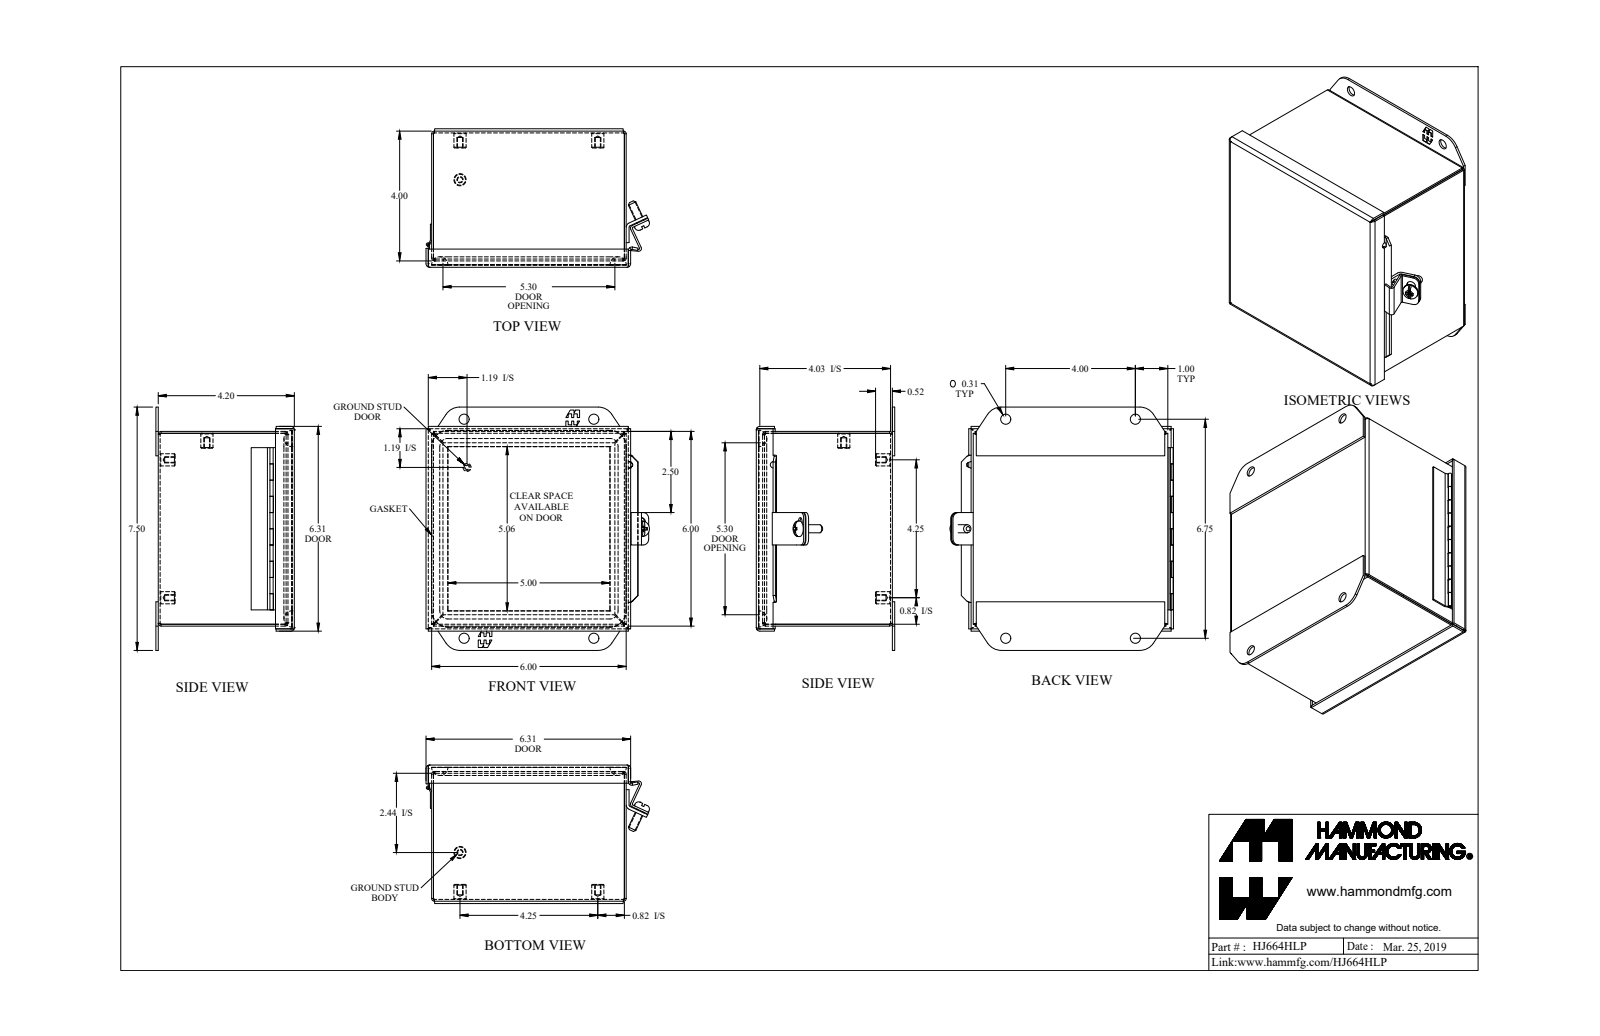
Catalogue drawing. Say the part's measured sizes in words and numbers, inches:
The part is named "HJ664HLP". Its 3-D file was written by "SolidWorks 2018 (AUTOMOTIVE_DESIGN)". It is 16 solids with 566 faces: 305 planar, 163 cylindrical and 98 other. Overall it measures 7.5 by 6.892 by 4.269 inches. Its volume is 15.42 cubic inches and its surface area 490 square inches. Round holes: 5 of diameter 0.156, 4 of diameter 0.313, 1 of diameter 0.05, 1 of diameter 0.213. Round bosses or shafts: 5 of diameter 0.375, 2 of diameter 0.25, 1 of diameter 0.48, 1 of diameter 0.188, 1 of diameter 0.1. Partial cylindrical surfaces (rounded edges, fillets, slot ends): 14 of radius 0.188, 10 of radius 0.029, 10 of radius 0.086, 5 of radius 0.036, 5 of radius 0.108, 4 of radius 0.25, 4 of radius 0.499, 4 of radius 0.5. The main face-to-face distances are 0.057, 5.943, 0.072, 4.197, 4.125, 6, 5.886, 0.057, 4.068, 4.14. The hole center spacings are 1.256, 4.25, 4.31, 5.501, 6.874, 4, 6.01, 6.75.
